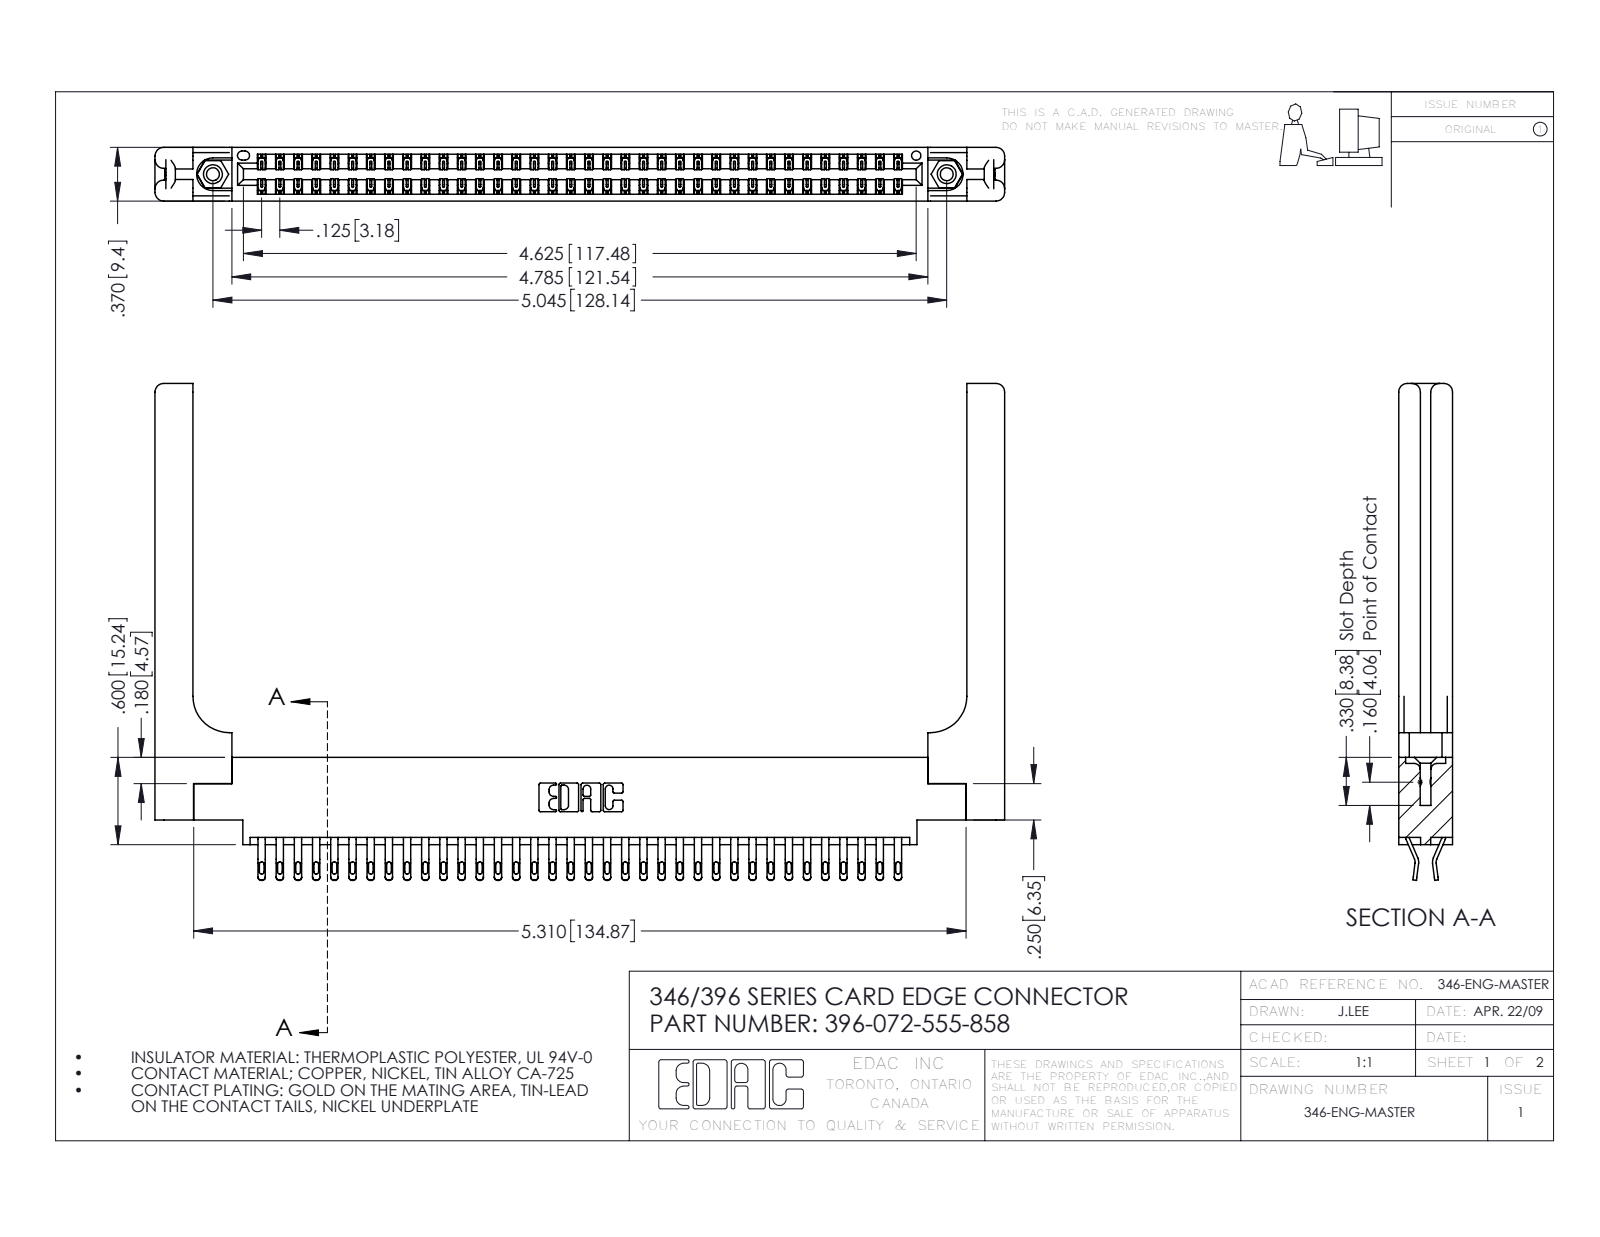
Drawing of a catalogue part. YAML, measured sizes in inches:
part_name: "346 Part_0.170 Offset - 0.156 Dia-TH; 396-072-555-858; 345-292-001_555 Tail; 345-250-001_345-250-001-102 (+1 more)"
step_written_by: "SolidWorks 2016 (CONFIG_CONTROL_DESIGN)"
units: inches
bodies: {solids: 77, faces: 4558, planar: 2604, cylindrical: 1894, other: 60}
overall_size: [5.841, 3.415, 0.37]
volume: 1.341
surface_area: 39.83
round_holes:
  - {diameter: 0.089, count: 2}
  - {diameter: 0.125, count: 2}
  - {diameter: 0.156, count: 2}
  - {diameter: 0.064, count: 1}
round_bosses_or_shafts:
  - {diameter: 0.155, count: 2}
partial_cylinders:
  - {radius: 0.016, count: 144}
  - {radius: 0.02, count: 144}
  - {radius: 0.006, count: 108}
  - {radius: 0.01, count: 22}
  - {radius: 0.06, count: 16}
  - {radius: 0.007, count: 6}
  - {radius: 0.031, count: 6}
  - {radius: 0.026, count: 3}
face_to_face_distances: [0.37, 0.048, 0.322, 0.072, 0.148, 0.15, 0.25, 0.025, 0.298, 0.275]
hole_center_spacings: [0.246, 4.836, 5.045]
